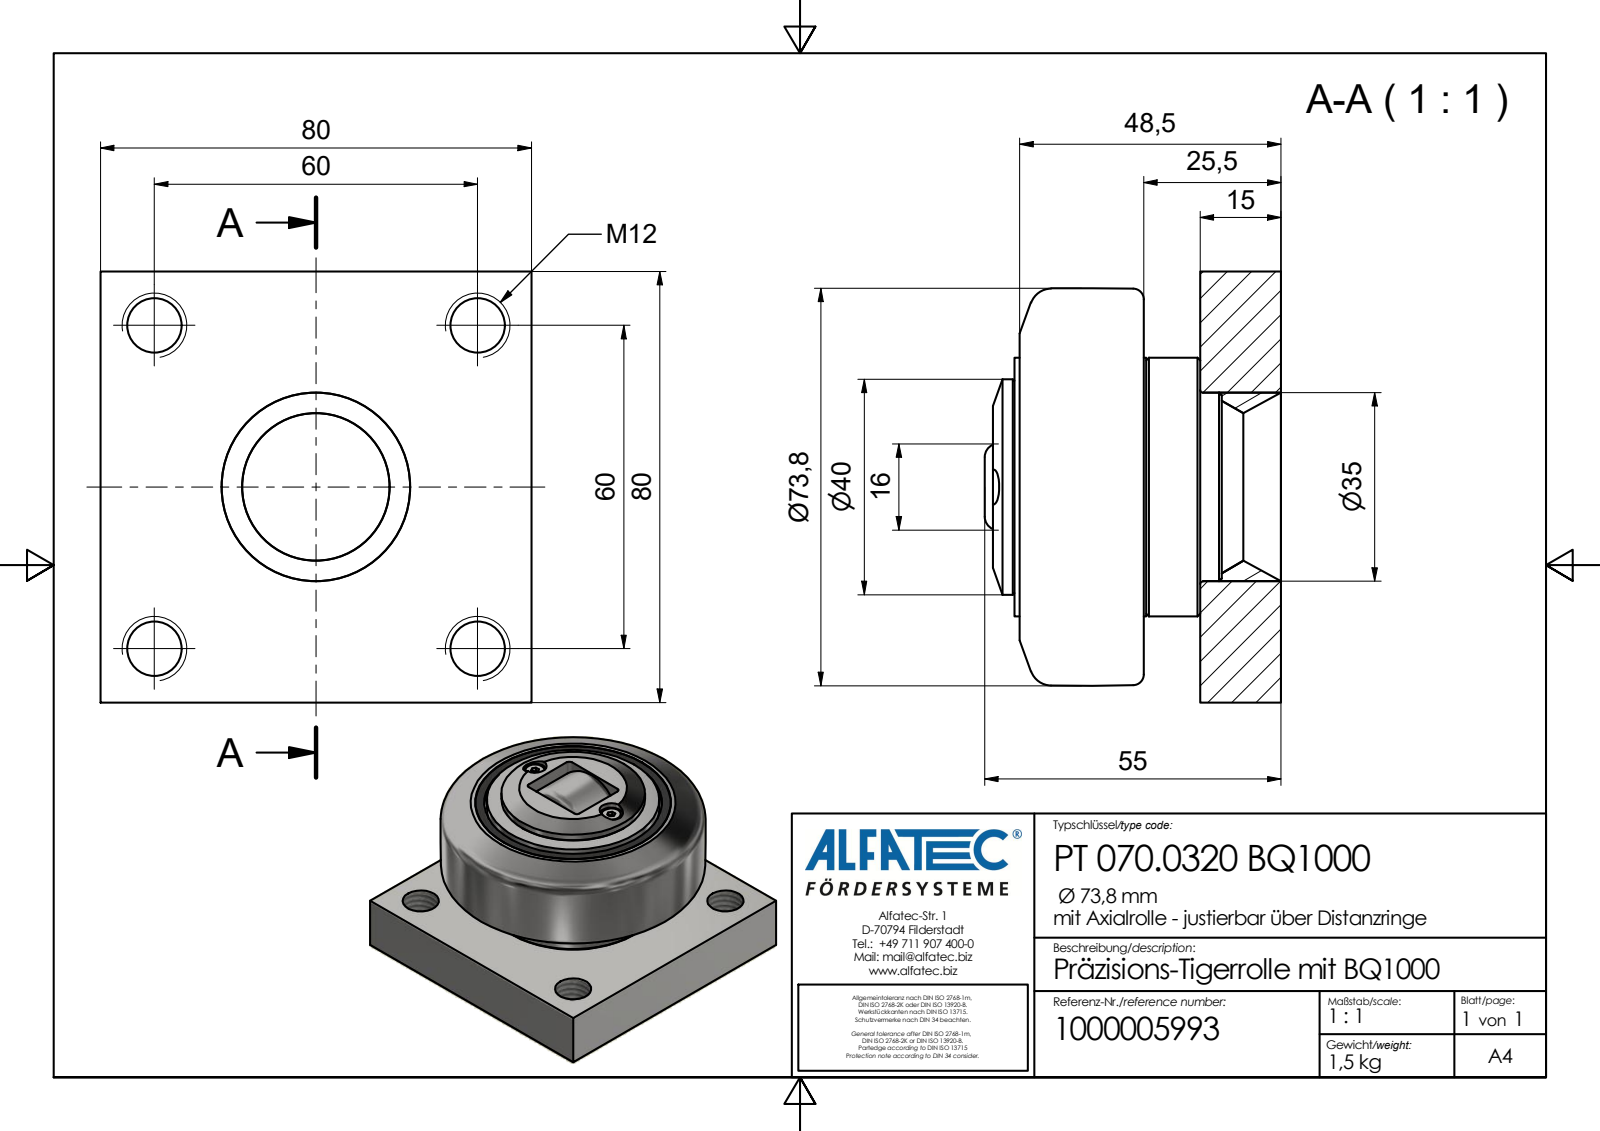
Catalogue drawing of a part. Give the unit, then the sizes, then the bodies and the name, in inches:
Units: inches
Overall size (bounding box): 3.15 × 3.15 × 2.165
Round holes (diameter × count): ⌀0.398 ×4, ⌀0.138 ×2, ⌀0.256 ×2, ⌀0.984 ×1, ⌀1.386 ×1
Round bosses / shafts (diameter × count): ⌀0.211 ×2, ⌀0.118 ×2, ⌀1.89 ×1, ⌀1.575 ×1, ⌀1.378 ×1
Partial cylindrical surfaces — rounded edges, fillets, slot ends (radius × count): R0.039 ×4, R0.201 ×1, R0.217 ×1, R0.256 ×1, R0.315 ×1, R0.491 ×1
Main face-to-face distances: 0.591, 3.15, 1.004, 0.413, 1.949, 1.358, 0.945, 1.909, 0.039, 1.319
Hole centre spacings: 1.32, 1.67, 2.129, 2.362, 0.591, 3.341, 1.181
Volume: 12.53 in³ · Surface area: 50.86 in²
Bodies: 1 solid, 108 faces (45 planar, 38 cylindrical, 25 other)
Part name (STEP PRODUCT): PT 070.0320 BQ1000_Kontur
STEP written by: Autodesk Inventor 2020 (AP242_MANAGED_MODEL_BASED_3D_ENGINEERING_MIM_LF)
